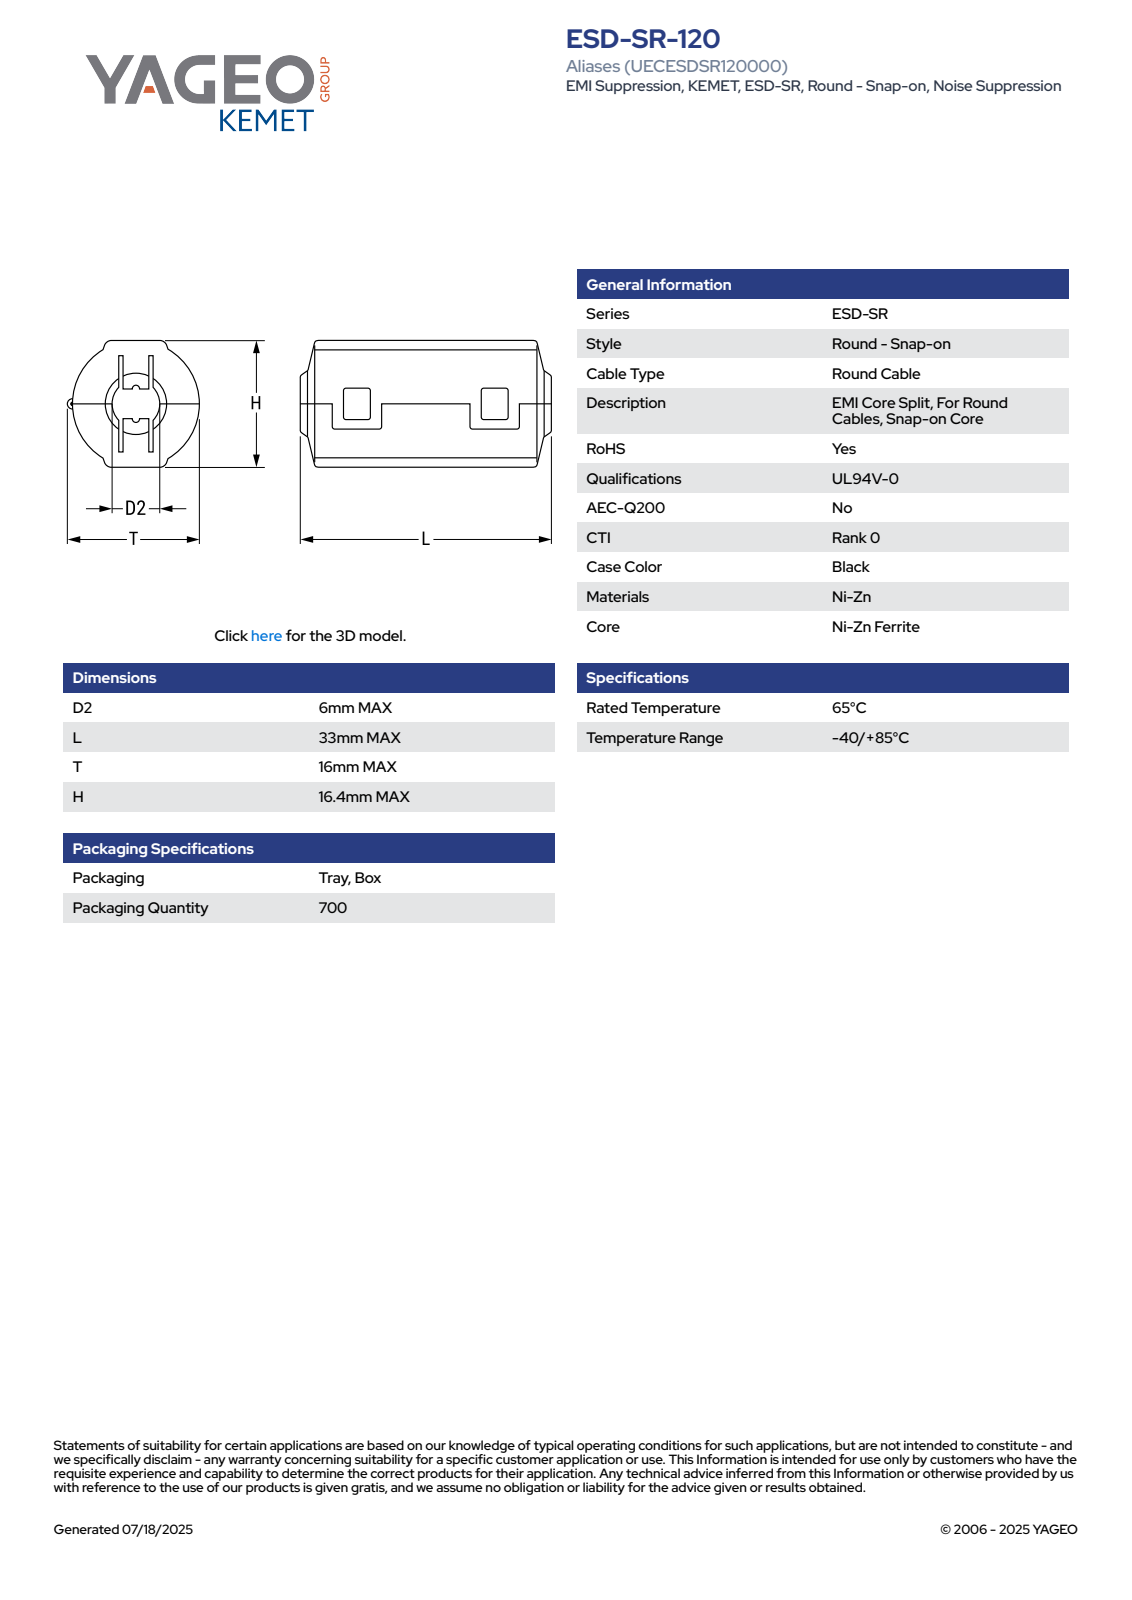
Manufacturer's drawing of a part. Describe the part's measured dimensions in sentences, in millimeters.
The part is named "EC_ESDSR_D26L33T16H16.4". Its 3-D file was written by "SolidWorks 2014 (AUTOMOTIVE_DESIGN)". It is 1 solid with 92 faces: 72 planar, 6 cylindrical and 14 other. Overall it measures 33 by 16.41 by 16 millimeters. Its volume is 6 111 cubic millimeters and its surface area 2 693 square millimeters. Partial cylindrical surfaces (rounded edges, fillets, slot ends): 2 of radius 3.03, 1 of radius 8. The main face-to-face distances are 16.4, 6.17, 10.23, 11.64, 4.06, 2.25, 30.75, 33, 28.5, 4.2.
